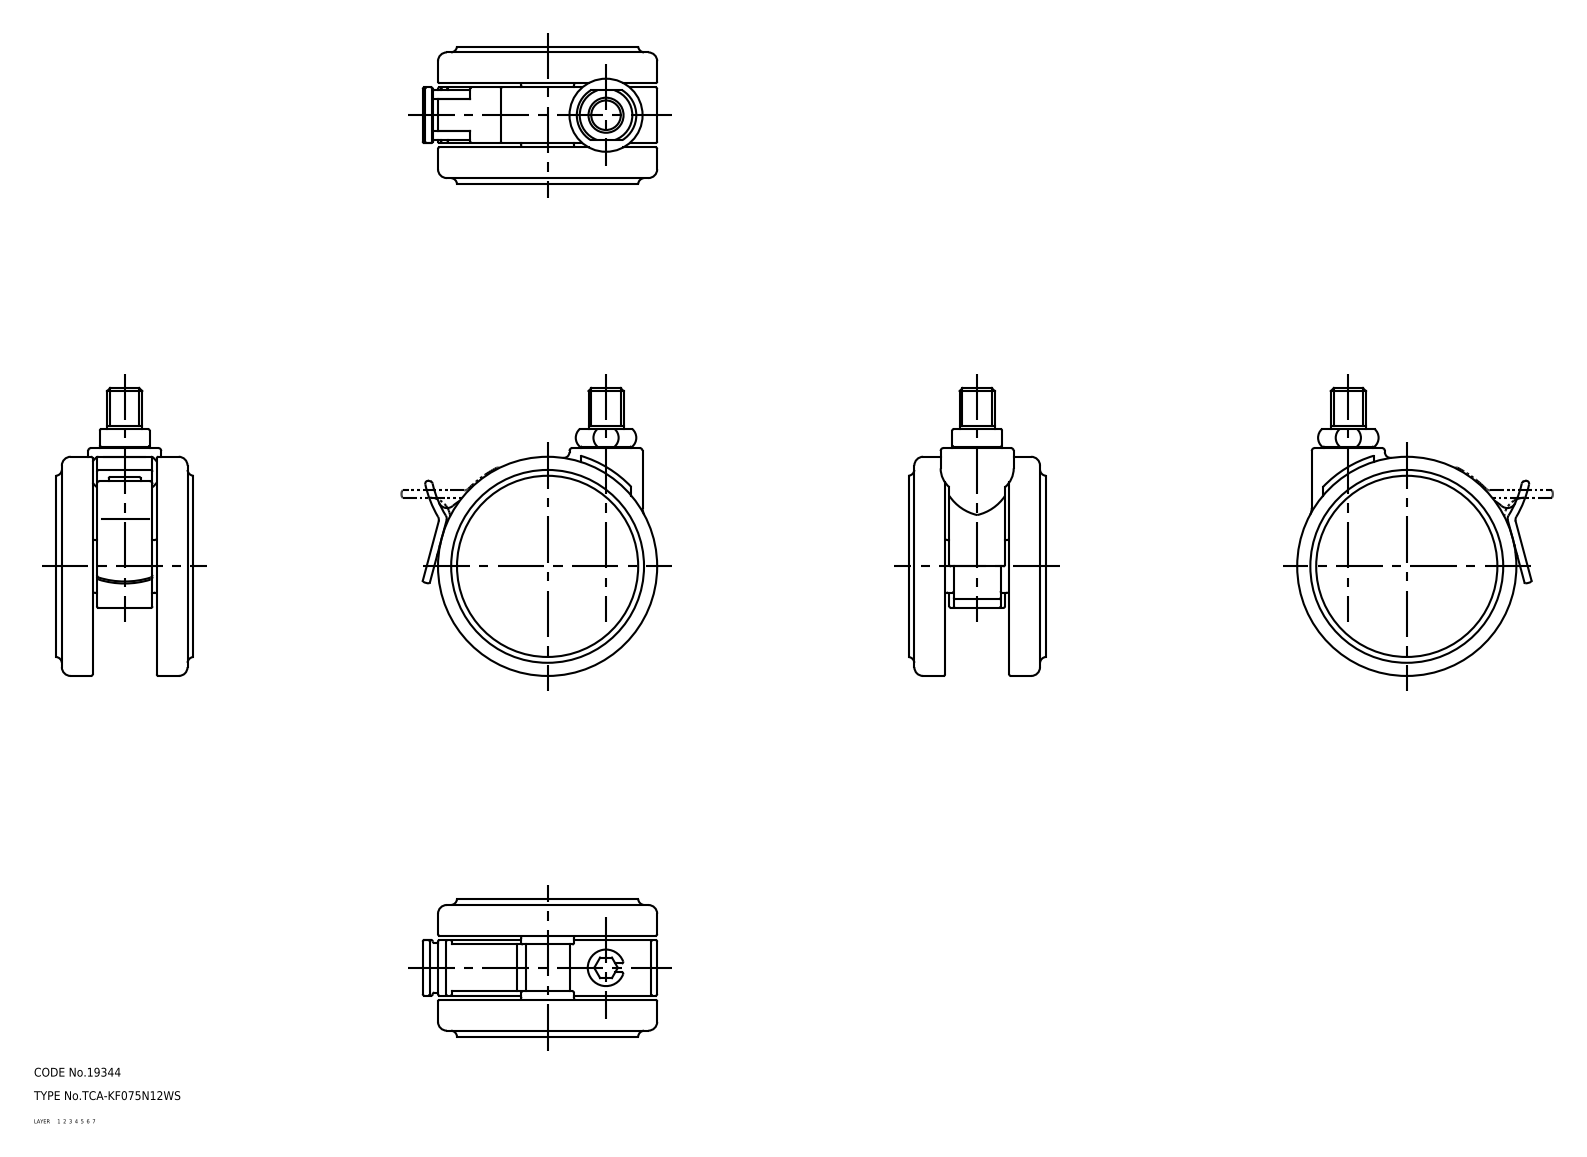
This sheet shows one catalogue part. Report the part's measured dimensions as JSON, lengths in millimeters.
{"part_name": "main shaft; wheel; wheel_mr; lever (+1 more)", "step_written_by": "SolidWorks 2015 (AUTOMOTIVE_DESIGN)", "units": "millimeters", "bodies": {"solids": 5, "faces": 269, "planar": 62, "cylindrical": 107, "other": 100}, "overall_size": [98.5, 80.25, 47], "volume_mm3": 155929, "surface_area_mm2": 39602, "round_holes": [[6, 1], [43, 1]], "round_bosses_or_shafts": [[75, 1], [25, 1], [18, 1], [17, 1], [12.5, 1], [12, 1]], "partial_cylinders_radius": [[0.5, 43], [1, 2], [2, 2], [3, 2], [35.5, 2], [2.89, 1], [7, 1], [7.54, 1]], "face_to_face_distances": [12.5, 34.5, 1.5, 22, 3, 14, 19, 20.5, 47, 33]}
